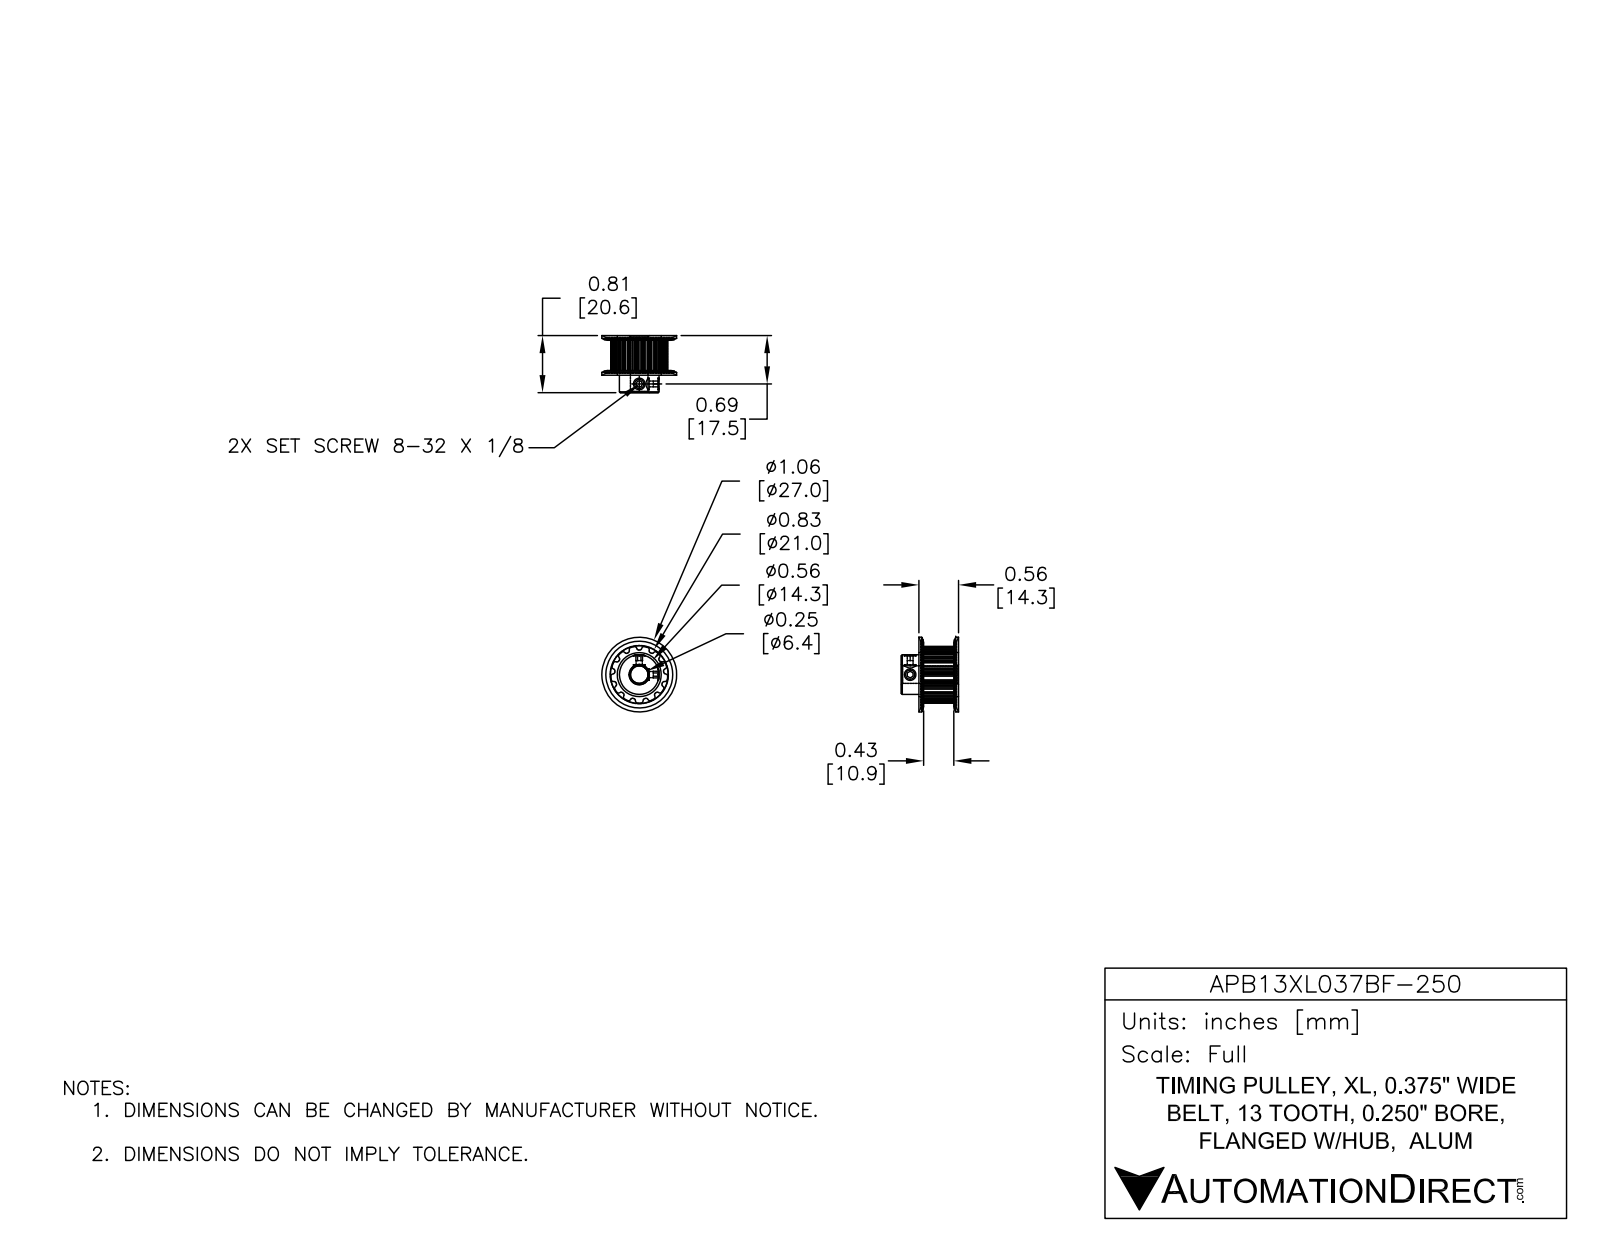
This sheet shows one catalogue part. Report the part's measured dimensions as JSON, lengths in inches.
{"part_name": "APB13XL037BF-250", "step_written_by": "SolidWorks 2014 (AUTOMOTIVE_DESIGN)", "units": "inches", "bodies": {"solids": 1, "faces": 151, "planar": 45, "cylindrical": 84, "other": 22}, "overall_size": [1.063, 1.063, 0.813], "volume_in3": 0.292, "surface_area_in2": 5.387, "round_holes": [[0.088, 2], [0.25, 1]], "round_bosses_or_shafts": [[0.563, 1]], "partial_cylinders_radius": [[0.015, 52], [0.349, 1]], "face_to_face_distances": [0.495, 0.033, 0.528, 0.813, 0.78, 0.285, 0.065, 0.032, 0.463, 0.748]}
